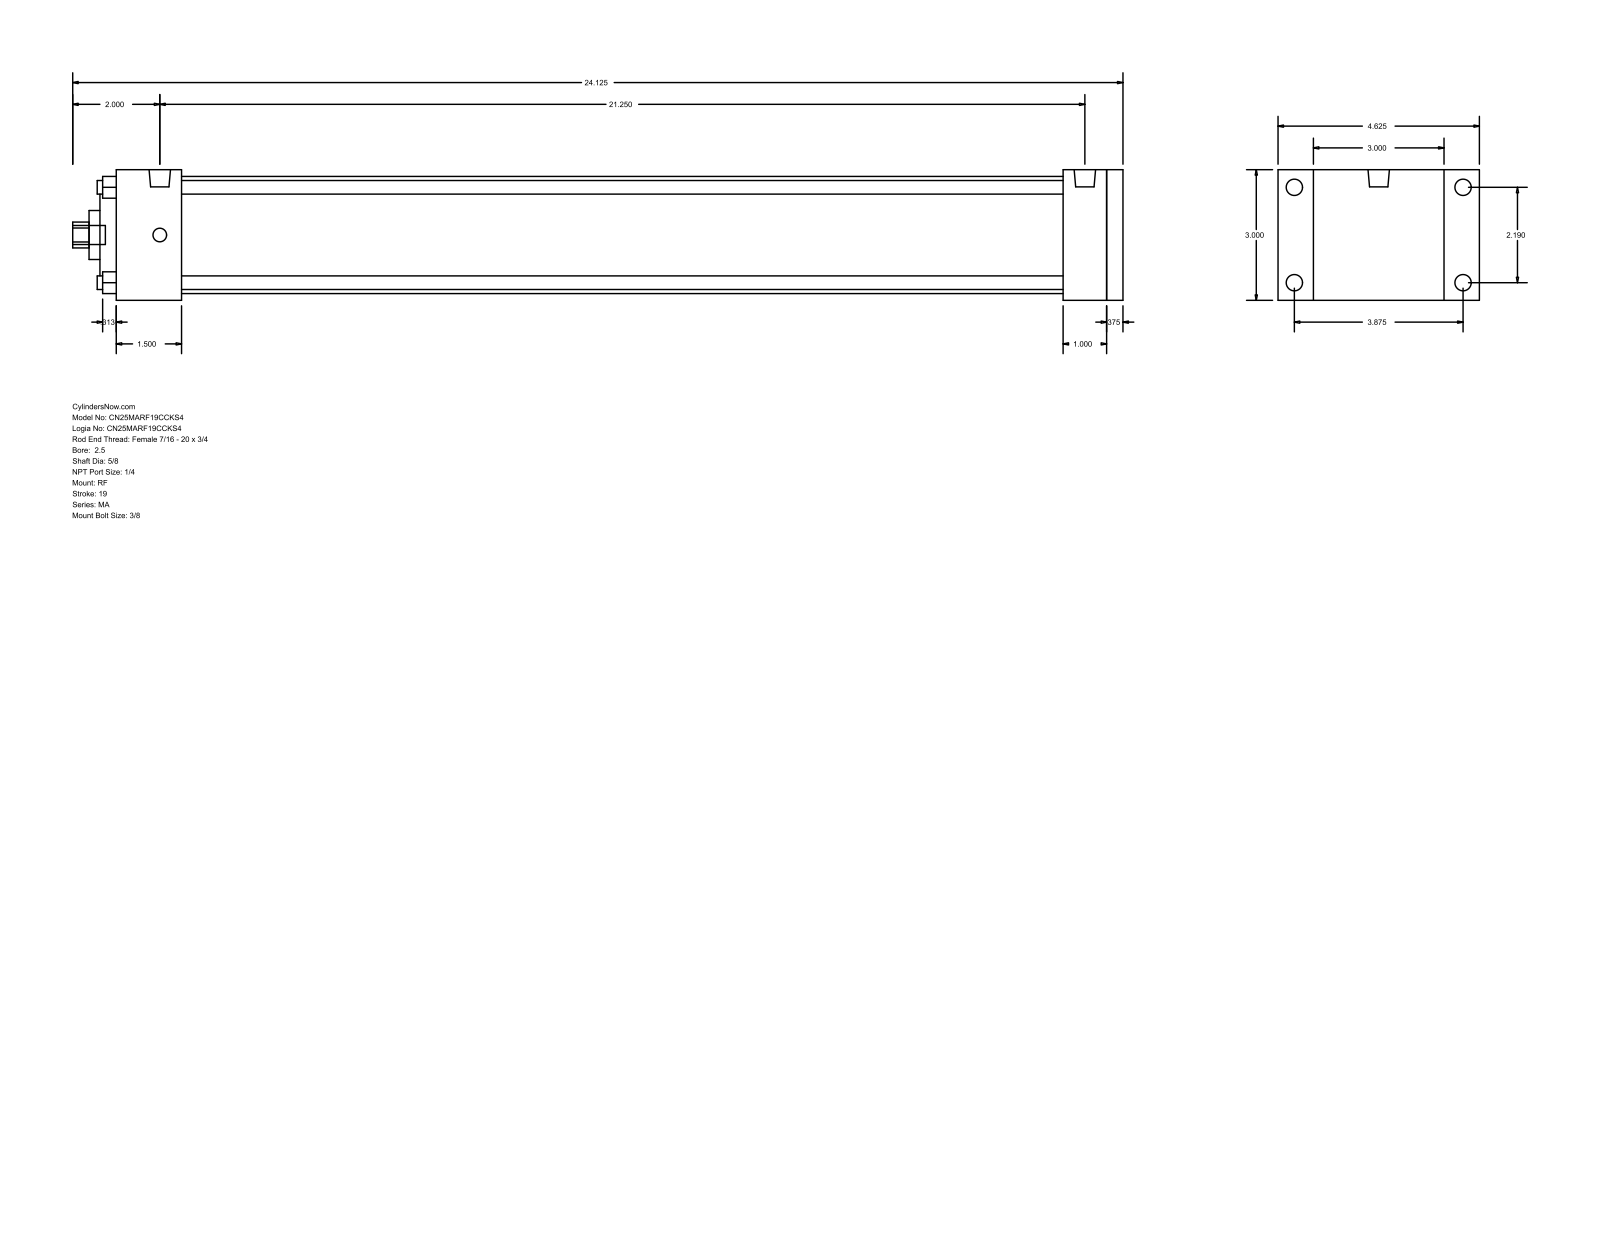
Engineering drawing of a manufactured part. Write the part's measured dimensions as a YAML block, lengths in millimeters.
part_name: "MA_RF__0250_0.625"
step_written_by: "GSSL Pune (CONFIG_CONTROL_DESIGN)"
units: millimeters
bodies: {solids: 0, faces: 94, planar: 65, cylindrical: 29, other: 0}
overall_size: [612.77, 117.47, 76.2]
round_holes:
  - {diameter: 7.94, count: 4}
  - {diameter: 15.88, count: 1}
  - {diameter: 28.57, count: 1}
  - {diameter: 50.8, count: 1}
  - {diameter: 68.33, count: 1}
round_bosses_or_shafts:
  - {diameter: 9.53, count: 4}
  - {diameter: 7.94, count: 4}
  - {diameter: 12.49, count: 2}
  - {diameter: 11.11, count: 1}
partial_cylinders:
  - {radius: 7.54, count: 1}
face_to_face_distances: [76.2, 587.37, 9.52, 577.85, 25.4, 38.1, 552.45, 514.35, 539.75, 549.27]
hole_center_spacings: [39.33, 55.62, 78.66]
